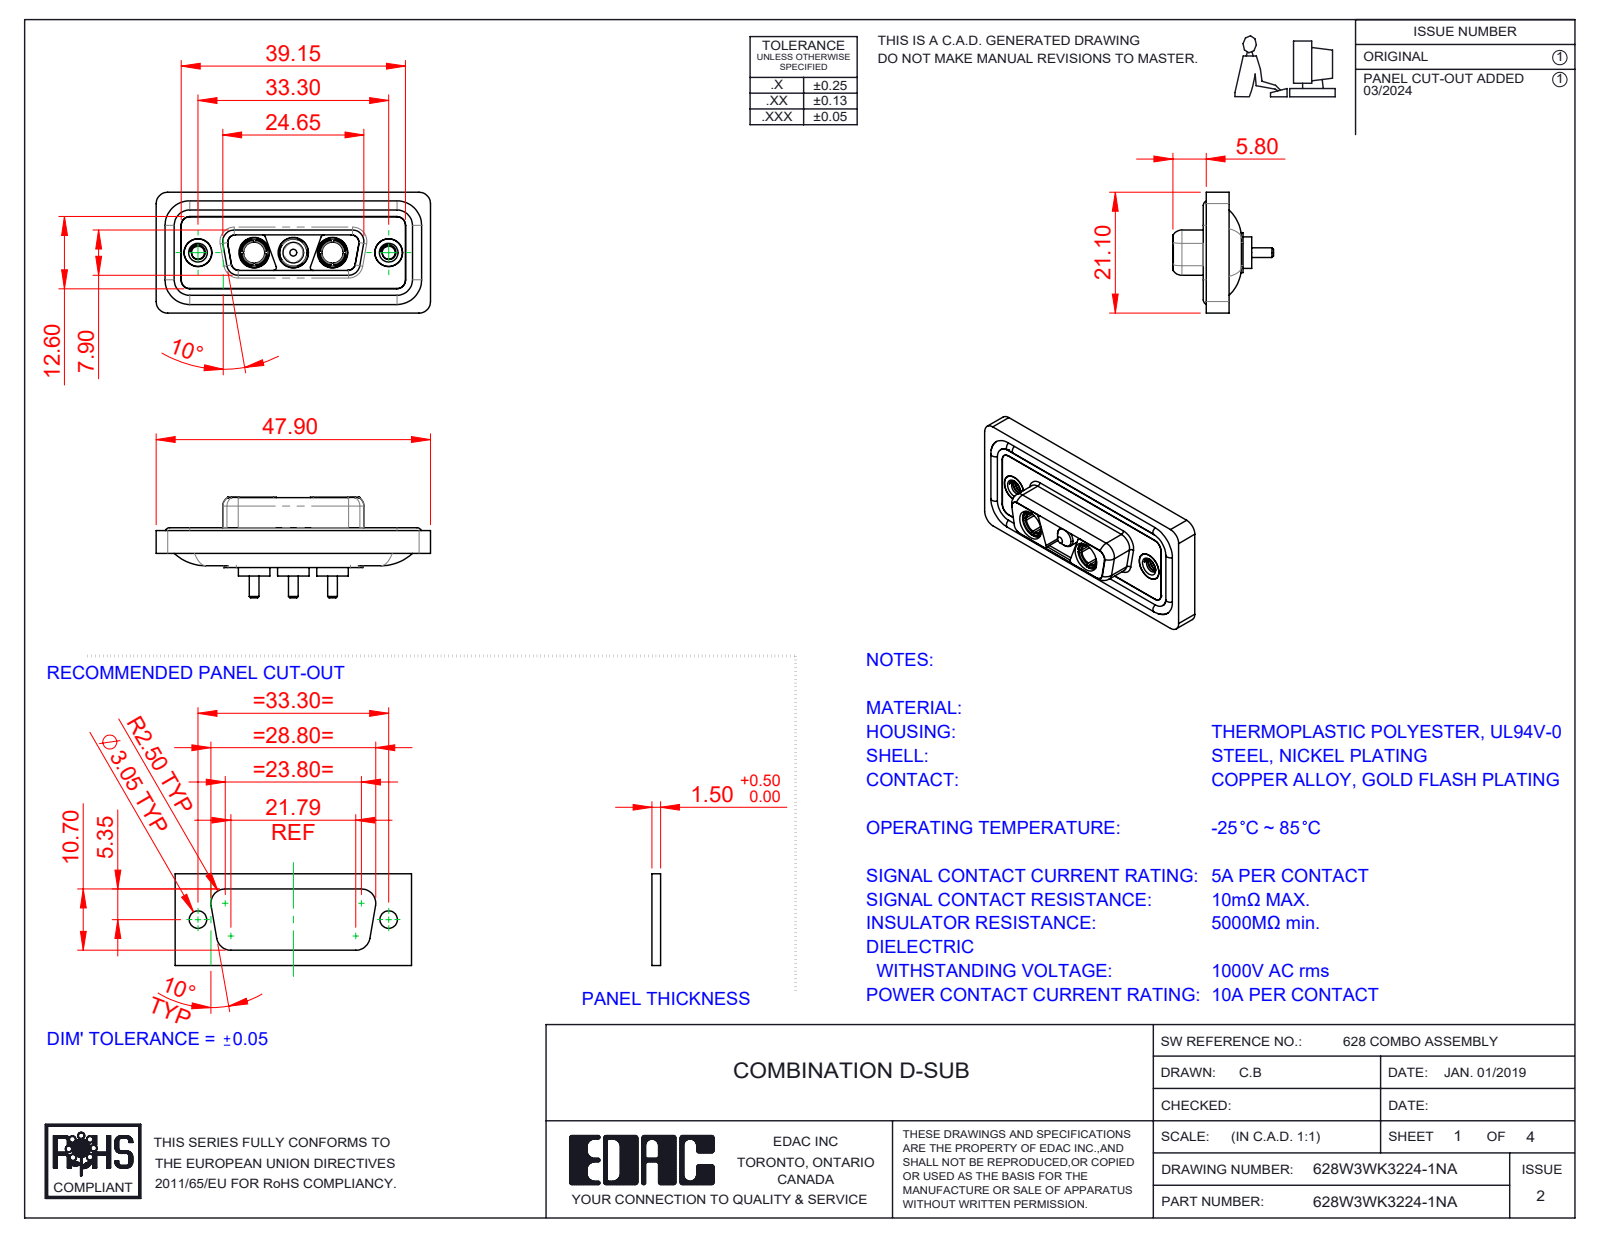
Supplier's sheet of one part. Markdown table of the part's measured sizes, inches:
| quantity | value |
| --- | --- |
| part name | Power Socket_10A S; 628Combo Housing_3WK3; Power Pin_10A S; 628Combo Shell Rear_15 Contacts (+4 more) |
| STEP written by | SolidWorks 2023 (CONFIG_CONTROL_DESIGN) |
| units | inches |
| bodies | 13 solids, 581 faces (178 planar, 260 cylindrical, 143 other) |
| overall size | 1.886 × 0.831 × 0.691 |
| volume | 0.356 in³ |
| surface area | 14.67 in² |
| round holes (diameter × count) | 0.191 × 5, 0.209 × 3, 0.089 × 2, 0.146 × 2, 0.157 × 2, 0.159 × 2, 0.197 × 2 |
| round bosses / shafts (diameter × count) | 0.063 × 4, 0.217 × 3, 0.205 × 3, 0.187 × 3, 0.148 × 3, 0.067 × 3, 0.195 × 2, 0.195 × 2 |
| partial cylindrical surfaces (radius × count) | 0.059 × 22, 0.079 × 20, 0.053 × 12, 0.02 × 8, 0.063 × 8, 0.01 × 4, 0.024 × 4, 0.026 × 4 |
| main face-to-face distances | 0.016, 0.063, 0.071, 0.02, 0.043, 0.114, 0.222, 0.278, 0.059, 0.211 |
| hole center spacings | 0.27, 0.386, 0.656, 0.925, 0.539, 1.311 |
